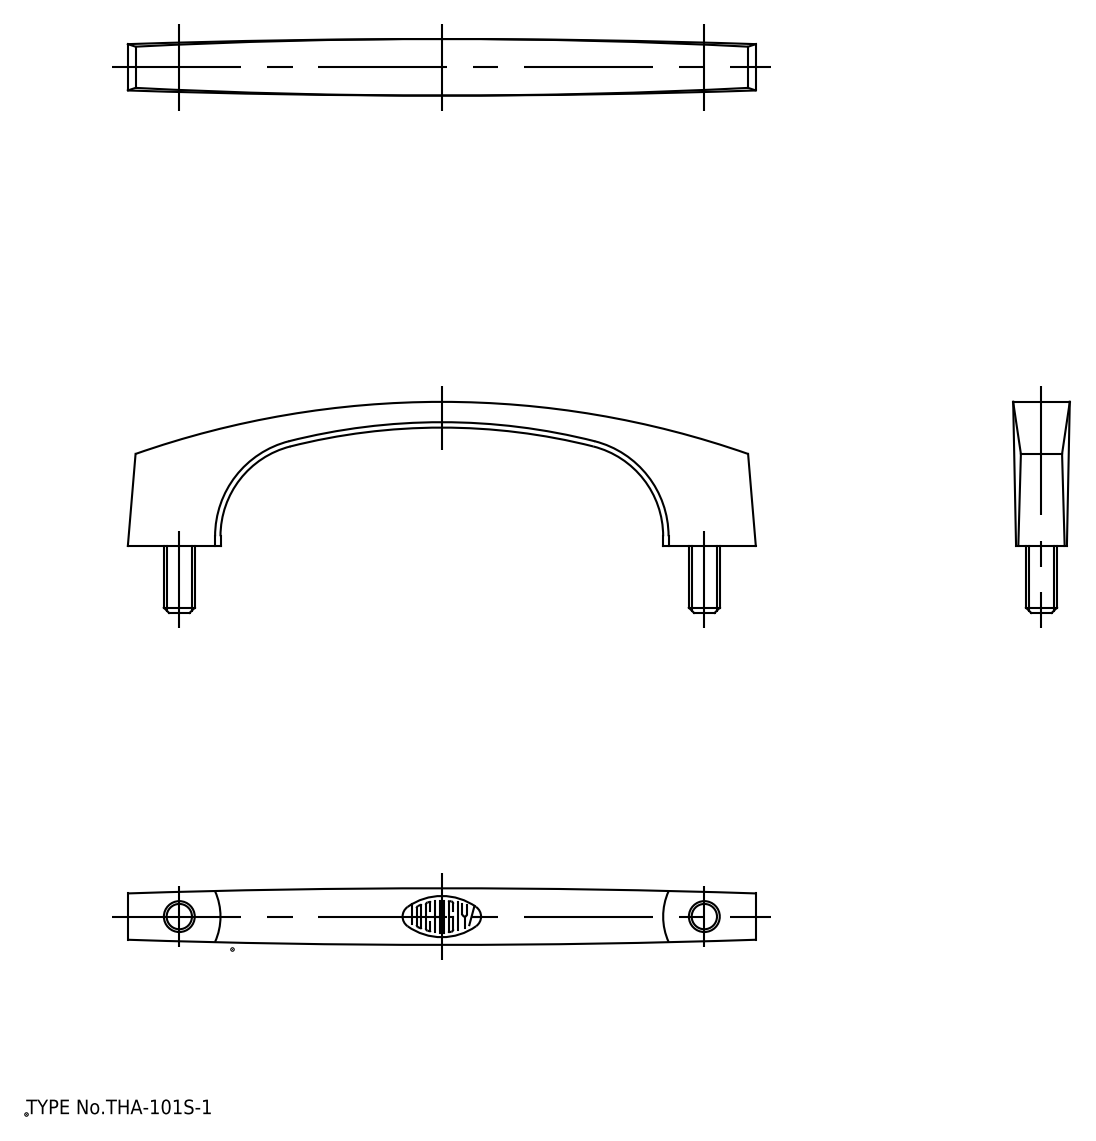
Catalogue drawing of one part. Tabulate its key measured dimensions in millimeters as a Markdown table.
| quantity | value |
| --- | --- |
| part name | screw; pull |
| STEP written by | spGate 19.8.4 (****-****-****-****) (AUTOMOTIVE_DESIGN) |
| units | millimeters |
| bodies | 3 solids, 30 faces (10 planar, 11 cylindrical, 9 other) |
| overall size | 122 × 41 × 11.01 |
| volume | 12 677 mm³ |
| surface area | 6 519 mm² |
| round holes (diameter × count) | 6 × 2 |
| partial cylindrical surfaces (radius × count) | 12 × 2, 180 × 1 |
| main face-to-face distances | 8, 21, 13 |
| hole center spacings | 102 |
